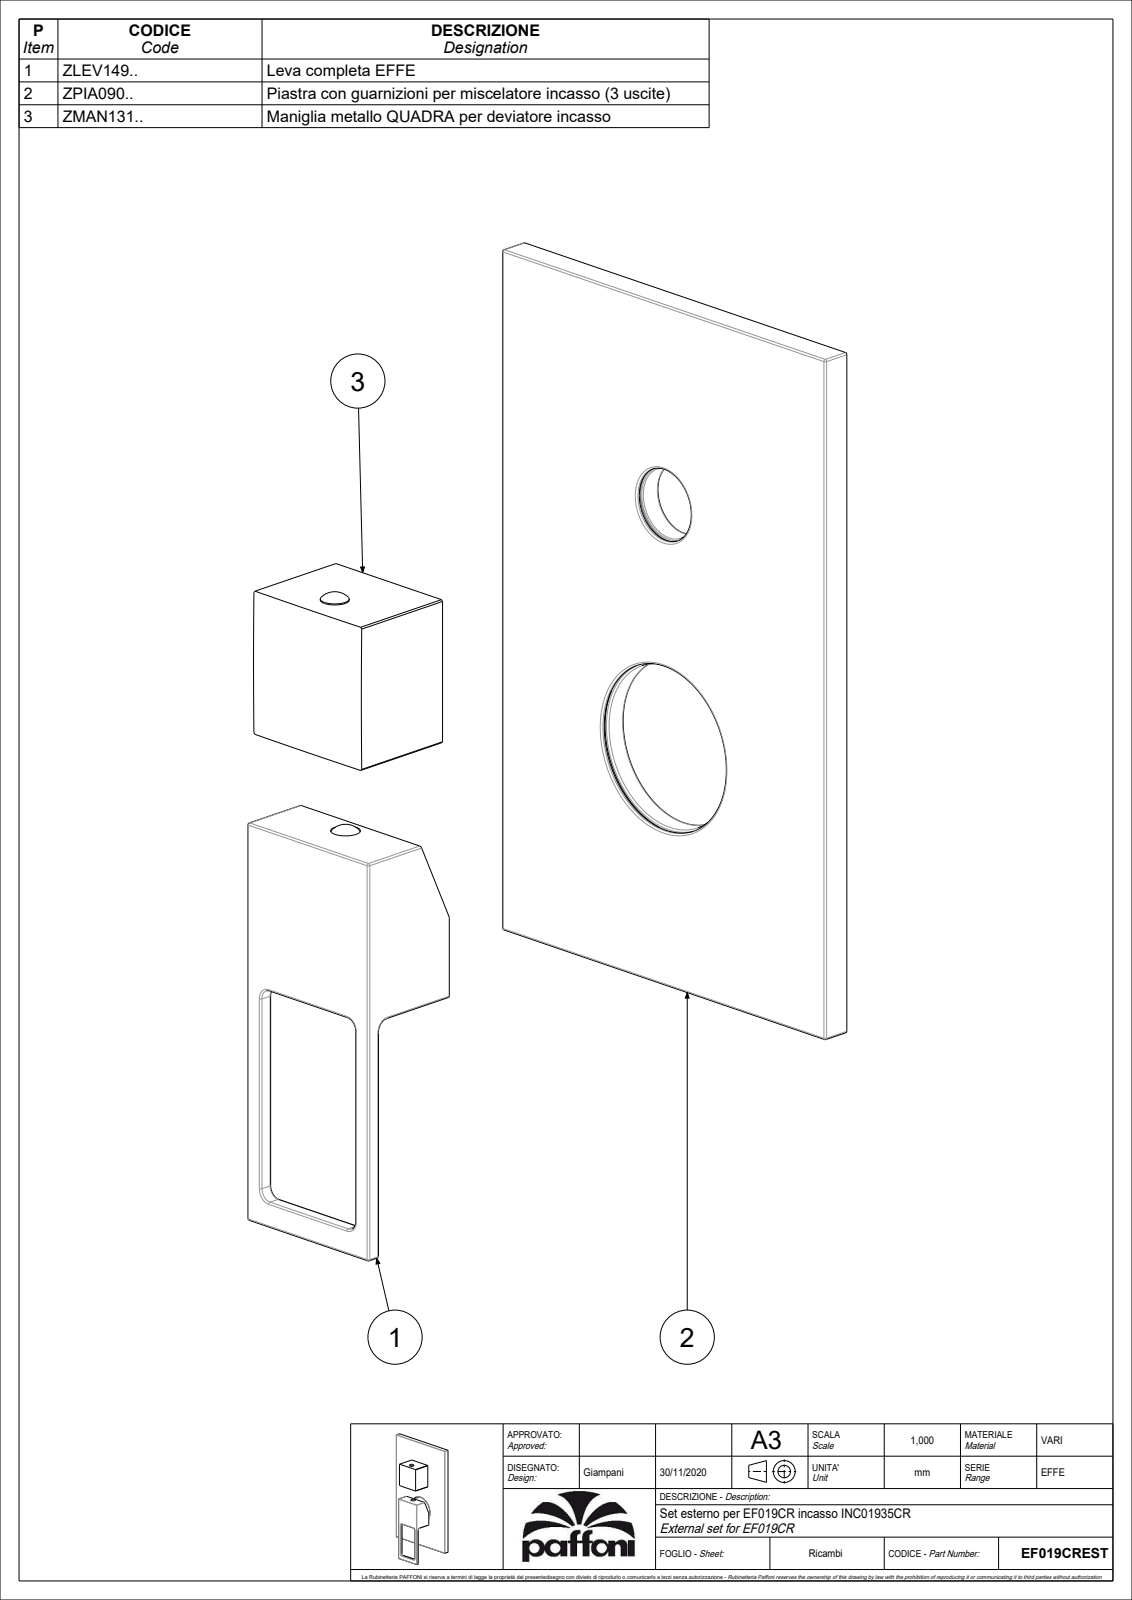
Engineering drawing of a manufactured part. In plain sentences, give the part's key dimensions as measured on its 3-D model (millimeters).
The part is named "EF018CREST". Its 3-D file was written by "CREO PARAMETRIC BY PTC INC, 2020044 (CONFIG_CONTROL_DESIGN)". It is 3 solids with 297 faces: 110 planar, 119 cylindrical and 68 other. Overall it measures 212.5 by 120 by 40.49 millimeters. Its volume is 158 894 cubic millimeters and its surface area 107 260 square millimeters. Round holes: 2 of diameter 3, 2 of diameter 5.5, 1 of diameter 3.2, 1 of diameter 4.2, 1 of diameter 4.5, 1 of diameter 7.8, 1 of diameter 14.8, 1 of diameter 19.2, 1 of diameter 20, 1 of diameter 21, 1 of diameter 23.2, 1 of diameter 36. Round bosses or shafts: 2 of diameter 7.6, 2 of diameter 5, 1 of diameter 51, 1 of diameter 49, 1 of diameter 25, 1 of diameter 23. Partial cylindrical surfaces (rounded edges, fillets, slot ends): 28 of radius 0.5, 8 of radius 1, 5 of radius 3, 1 of radius 4, 1 of radius 28. The main face-to-face distances are 2.5, 3, 8, 5, 5.5, 0.5, 40, 32, 2, 37.5. The hole center spacings are 4, 10, 58, 68.
